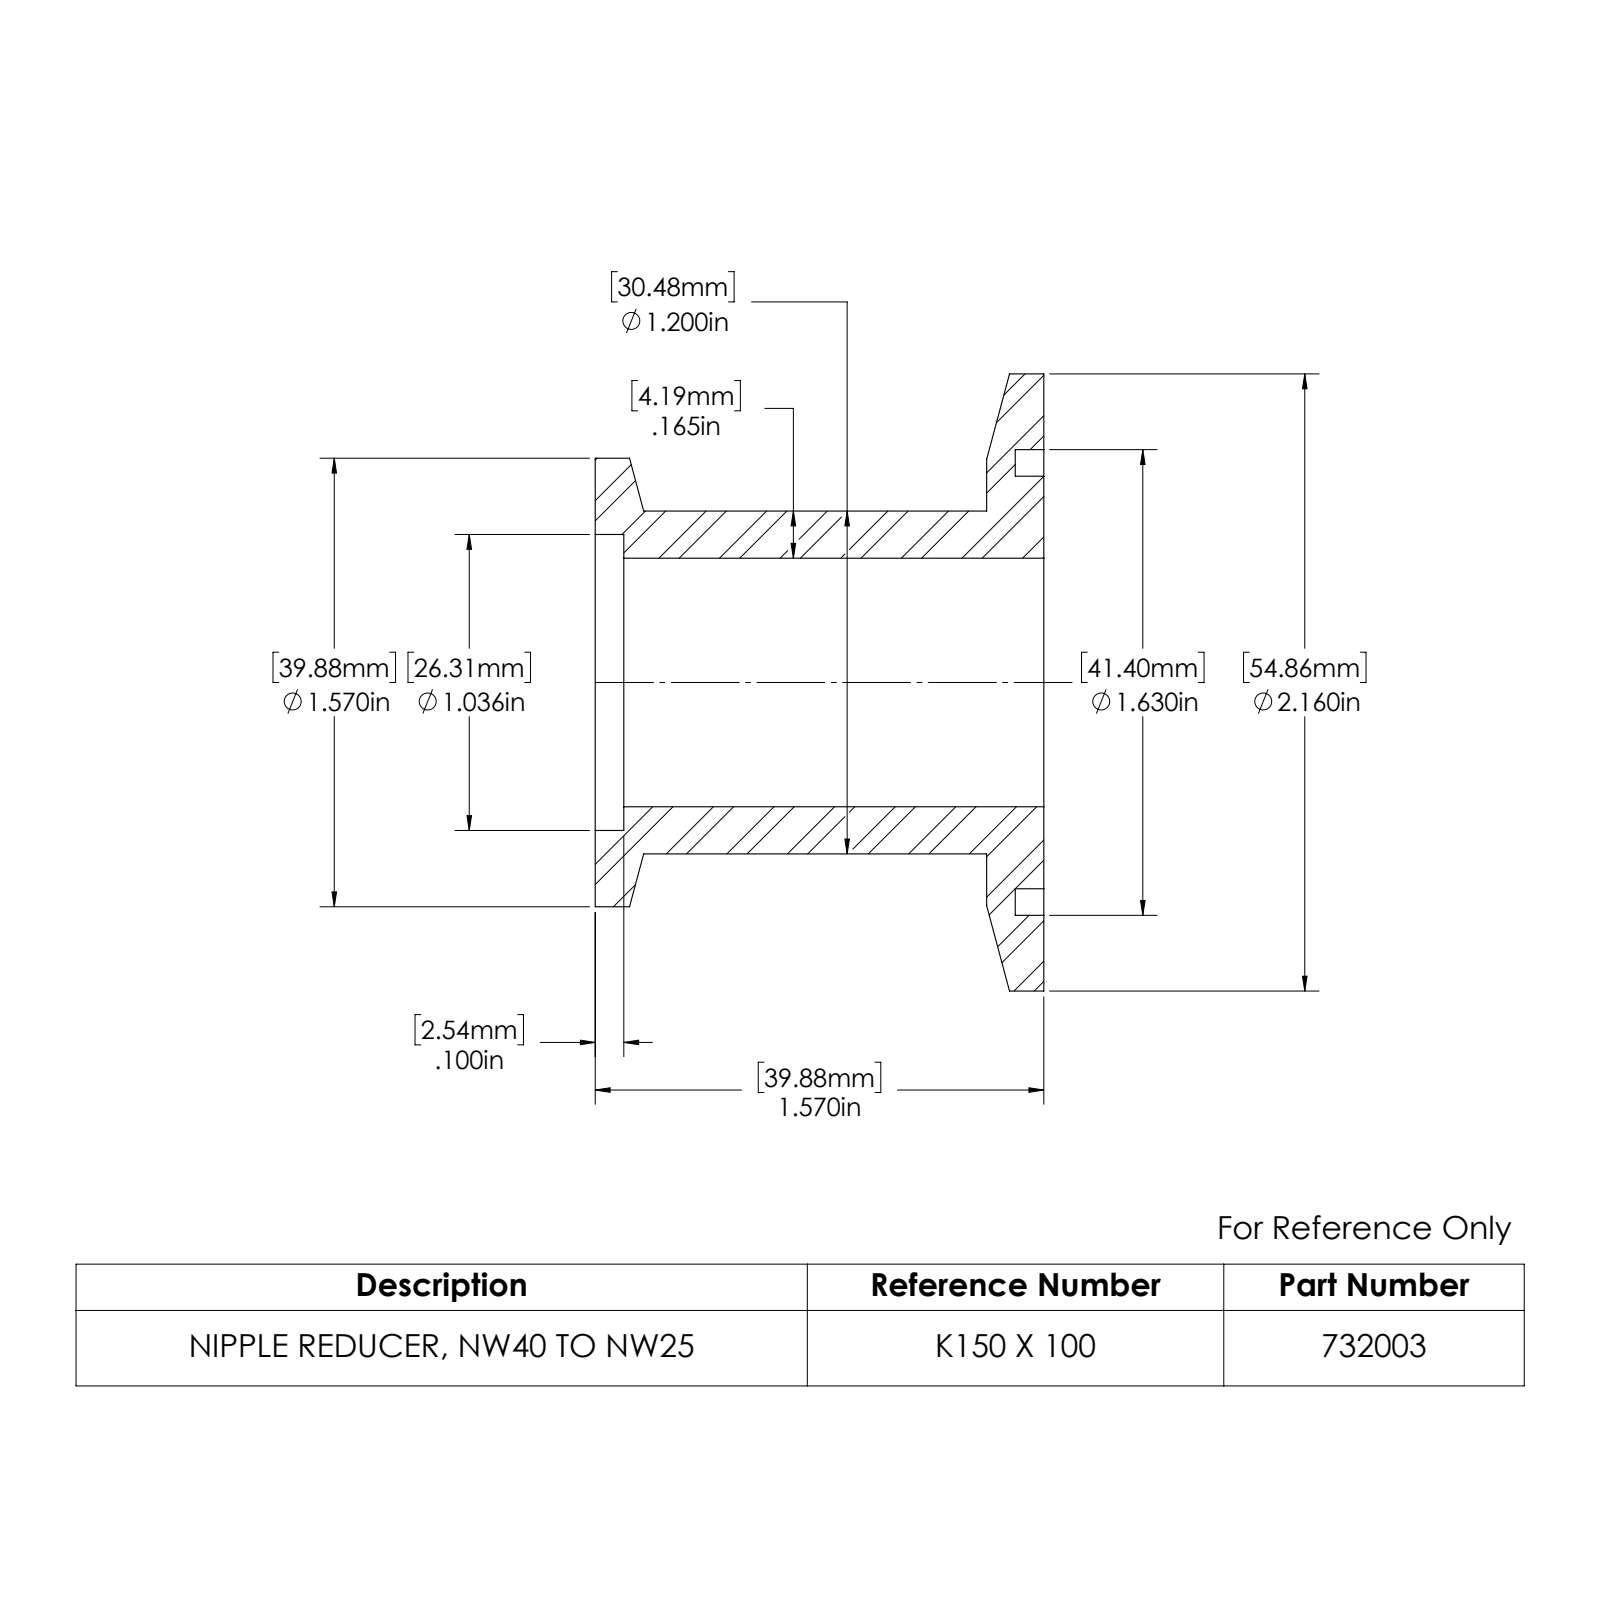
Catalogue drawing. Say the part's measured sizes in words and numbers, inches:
The part is named "732003". Its 3-D file was written by "SolidWorks 2022 (AUTOMOTIVE_DESIGN)". It is 1 solid with 24 faces: 6 planar, 14 cylindrical and 4 other. Overall it measures 2.16 by 2.16 by 1.57 inches. Its volume is 1.321 cubic inches and its surface area 19.08 square inches. Round holes: 1 of diameter 0.87, 1 of diameter 1.036, 1 of diameter 1.63. Round bosses or shafts: 1 of diameter 2.16, 1 of diameter 1.57, 1 of diameter 1.444, 1 of diameter 1.2. The main face-to-face distances are 0.1, 1.57, 1.37, 0.2, 1.47, 1.27.
